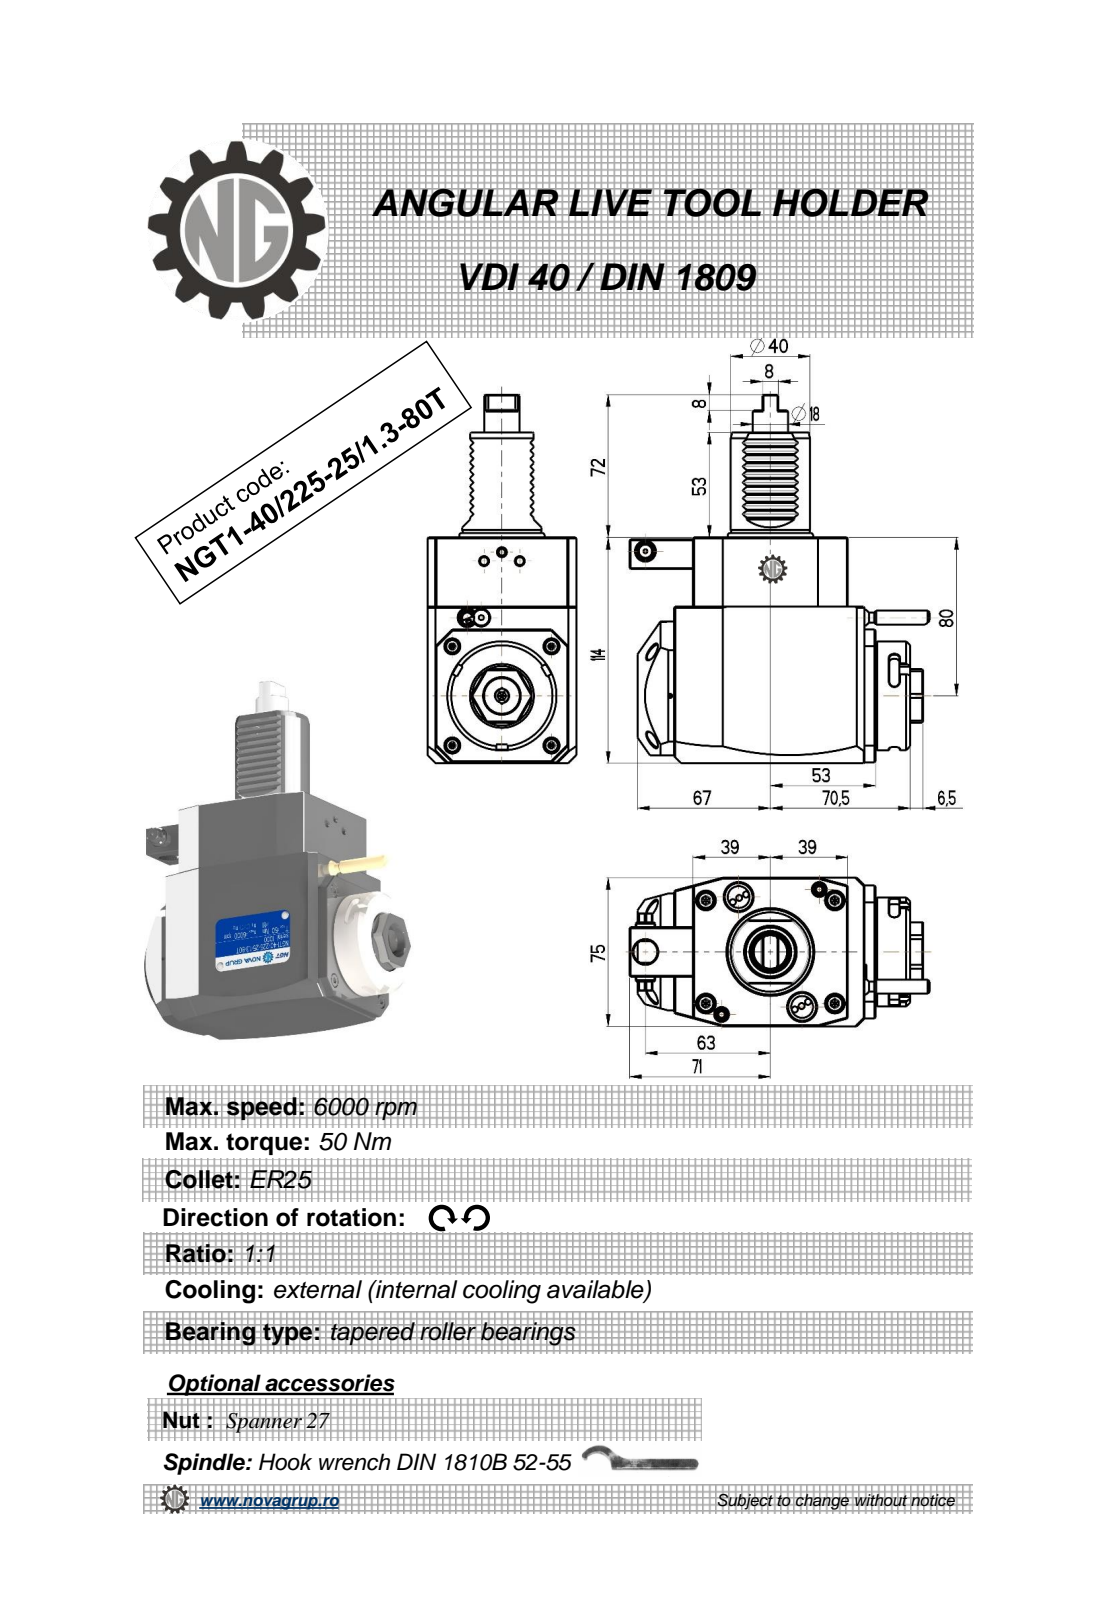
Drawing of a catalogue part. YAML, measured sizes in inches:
part_name: "NGT1_40_225_25_1_3_80T"
step_written_by: "PRO/ENGINEER BY PARAMETRIC TECHNOLOGY CORPORATION, 2010280 (CONFIG_CONTROL_DESIGN)"
units: inches
bodies: {solids: 1, faces: 399, planar: 222, cylindrical: 99, other: 78}
overall_size: [7.323, 5.958, 2.953]
volume: 57.69
surface_area: 109.8
round_holes:
  - {diameter: 0.079, count: 1}
  - {diameter: 0.098, count: 1}
  - {diameter: 0.118, count: 1}
  - {diameter: 0.177, count: 1}
  - {diameter: 0.374, count: 1}
  - {diameter: 0.472, count: 1}
  - {diameter: 0.709, count: 1}
round_bosses_or_shafts:
  - {diameter: 0.315, count: 2}
  - {diameter: 2.165, count: 1}
  - {diameter: 1.89, count: 1}
  - {diameter: 1.575, count: 1}
  - {diameter: 0.701, count: 1}
  - {diameter: 0.394, count: 1}
  - {diameter: 0.276, count: 1}
  - {diameter: 0.197, count: 1}
partial_cylinders:
  - {radius: 0.012, count: 20}
  - {radius: 0.098, count: 6}
  - {radius: 0.031, count: 2}
  - {radius: 7.087, count: 2}
  - {radius: 0.152, count: 1}
  - {radius: 0.167, count: 1}
  - {radius: 0.591, count: 1}
  - {radius: 0.965, count: 1}
face_to_face_distances: [2.953, 4.488, 0.551, 0.689, 3.071, 3.622, 1.24, 4.311, 1.378, 0.157]
hole_center_spacings: [1.47, 1.701, 2.854]
